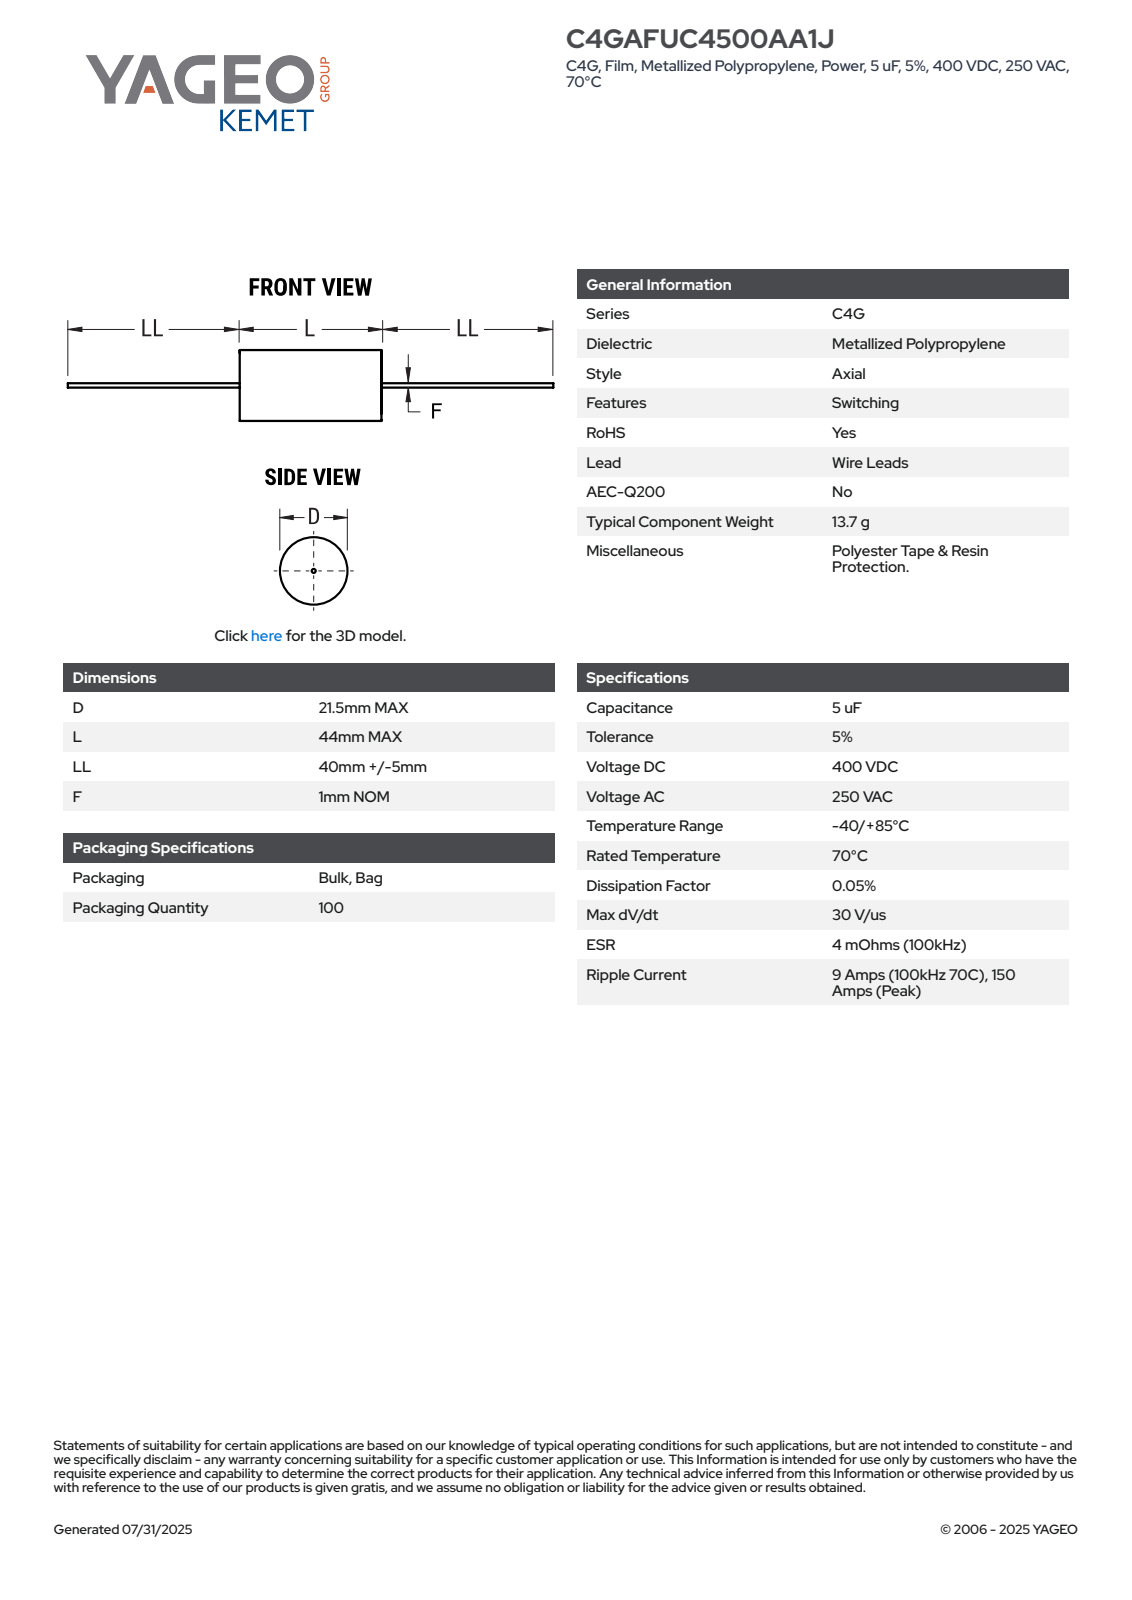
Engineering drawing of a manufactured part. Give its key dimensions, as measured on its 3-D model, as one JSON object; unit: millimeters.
{"part_name": "CFP_ACWF_21.5X44_D21.5L44LL45F1", "step_written_by": "SolidWorks 2014 (AUTOMOTIVE_DESIGN)", "units": "millimeters", "bodies": {"solids": 2, "faces": 87, "planar": 28, "cylindrical": 28, "other": 31}, "overall_size": [134, 21.5, 21.5], "volume_mm3": 16045, "surface_area_mm2": 4706, "round_bosses_or_shafts": [[21.5, 1], [1, 1]], "partial_cylinders_radius": [[10.74, 1]], "face_to_face_distances": [44, 43.99, 44.99, 45, 88.99, 134, 89.01, 89, 45.01]}
